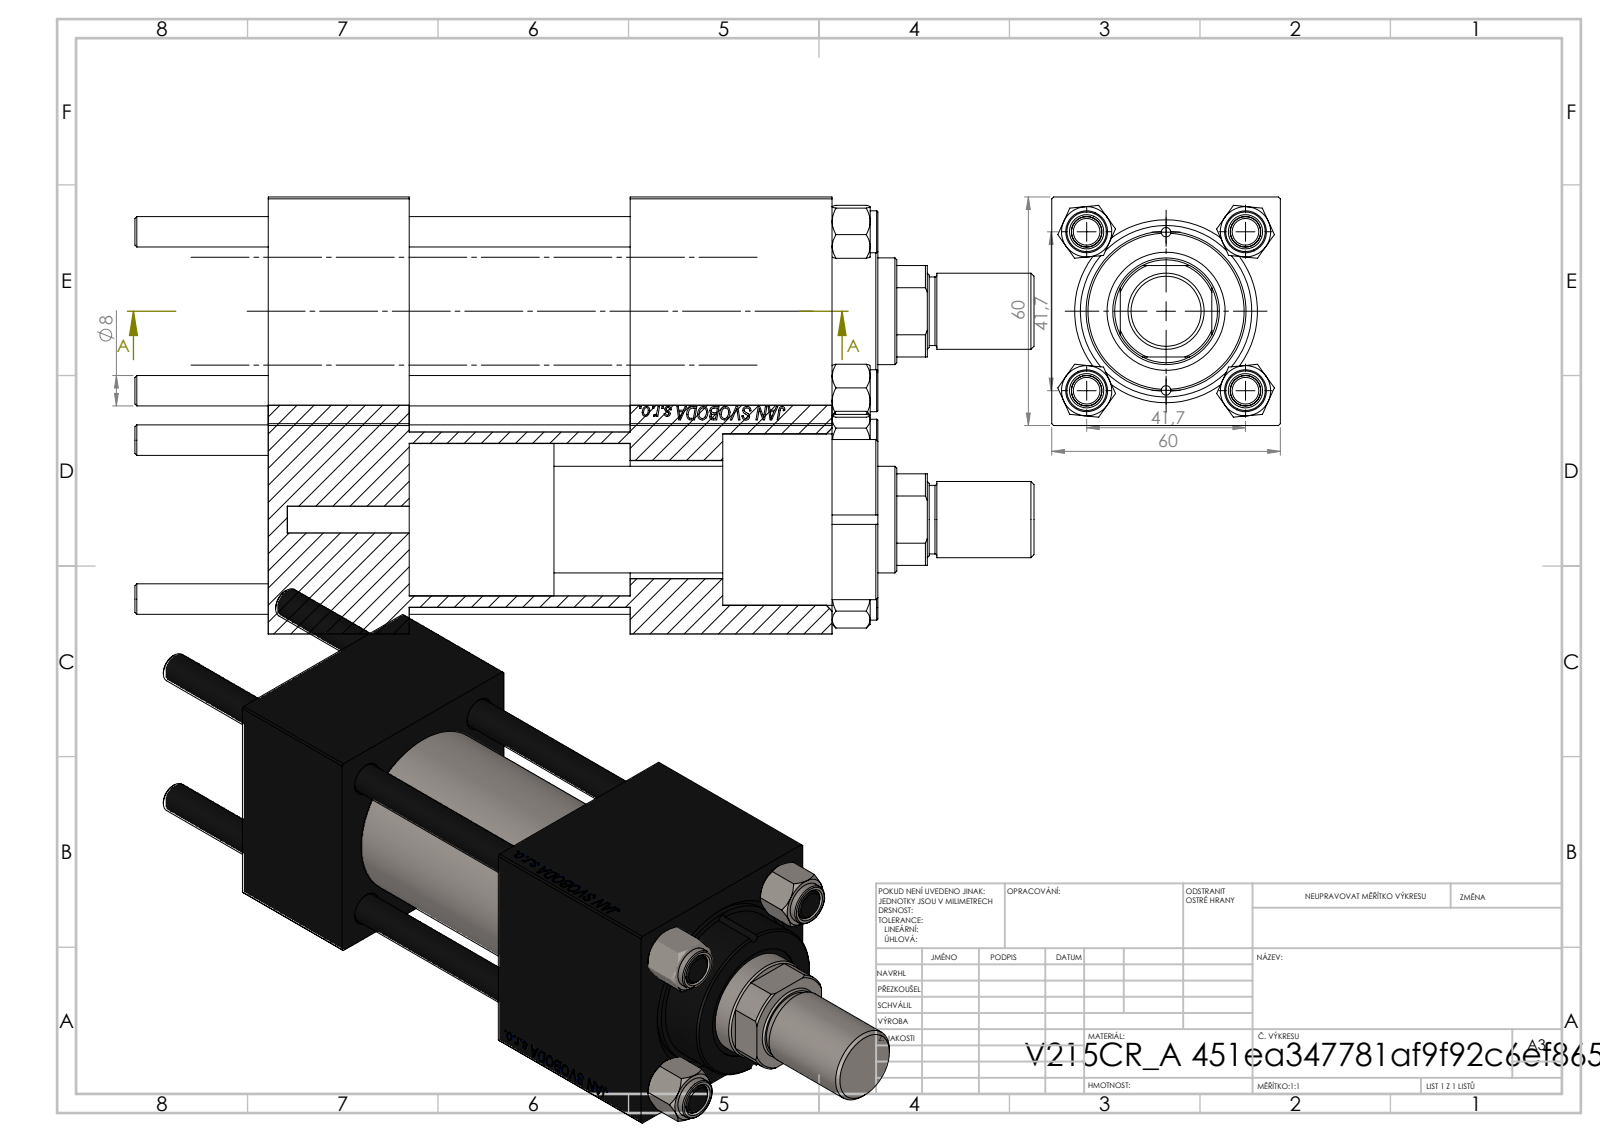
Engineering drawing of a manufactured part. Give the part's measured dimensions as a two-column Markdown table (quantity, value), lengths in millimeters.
| quantity | value |
| --- | --- |
| part name | CR025_012_A_0_G_A_G_M_020_+#_##_TYCINKA; V215CR_VCP; ROD_END_AH; V215CR_BODY_A (+2 more) |
| STEP written by | SolidWorks 2019 (CONFIG_CONTROL_DESIGN) |
| units | millimeters |
| bodies | 12 solids, 1155 faces (527 planar, 86 cylindrical, 542 other) |
| overall size | 236 × 60 × 60 |
| volume | 444 045 mm³ |
| surface area | 122 667 mm² |
| round holes (diameter × count) | 8 × 4, 2.5 × 2, 7 × 2, 16.66 × 2, 24 × 2, 18.5 × 1, 28 × 1, 31 × 1, 40 × 1, 45 × 1 |
| round bosses / shafts (diameter × count) | 11 × 4, 46 × 1, 42 × 1, 20 × 1, 18 × 1 |
| partial cylindrical surfaces (radius × count) | 13.5 × 1 |
| main face-to-face distances | 60, 37, 53, 58, 95, 148, 111, 119.3, 82.3, 24.3 |
| hole center spacings | 20.85, 29.49, 41.7, 46.53, 20.75, 58.97, 41.5, 92.5 |
